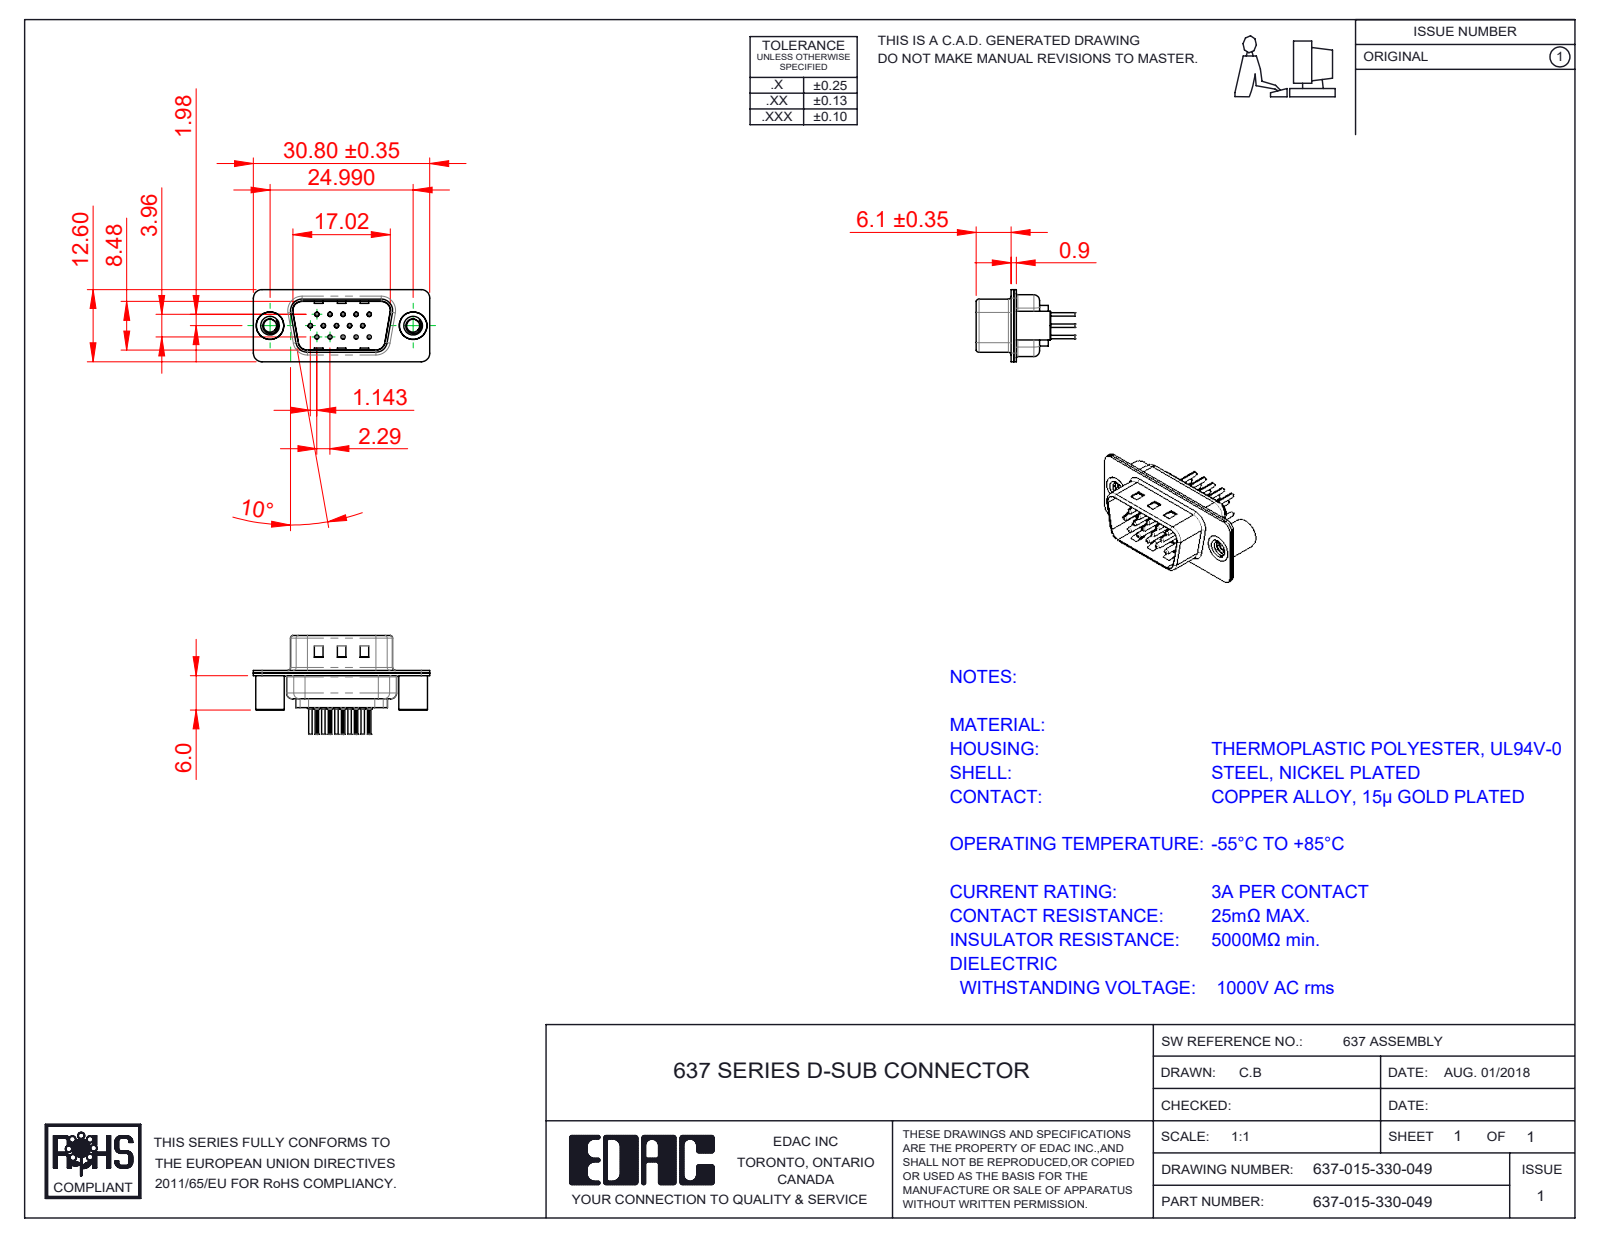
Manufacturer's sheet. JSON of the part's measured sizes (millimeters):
{"part_name": "637-015-330-049; 637 Shell Rear_15 Contacts; 637 Housing_15 Contacts; 637 Contact Row 3_30 (+4 more)", "step_written_by": "SolidWorks 2020 (CONFIG_CONTROL_DESIGN)", "units": "millimeters", "bodies": {"solids": 20, "faces": 1838, "planar": 469, "cylindrical": 712, "other": 657}, "overall_size": [30.8, 17.25, 12.6], "volume_mm3": 1379, "surface_area_mm2": 4840, "round_holes": [[0.2, 15], [0.35, 15], [1.1, 15], [1.6, 15], [2.26, 2], [4, 2], [4.8, 2]], "round_bosses_or_shafts": [[2, 15], [1.5, 15], [0.75, 15], [0.6, 15], [5, 2], [4.9, 2], [4.5, 2]], "partial_cylinders_radius": [[0.1, 30], [1.5, 16], [2, 12], [0.5, 8], [0.25, 4], [0.55, 4], [0.7, 4], [0.95, 4]], "face_to_face_distances": [0.45, 0.9, 0.4, 0.7, 8.88, 8.48, 1.05, 0.31, 4.55, 1.16], "hole_center_spacings": [3.96, 2.28, 4.57, 2.29, 6.05, 6.86, 7.92, 6.04]}
